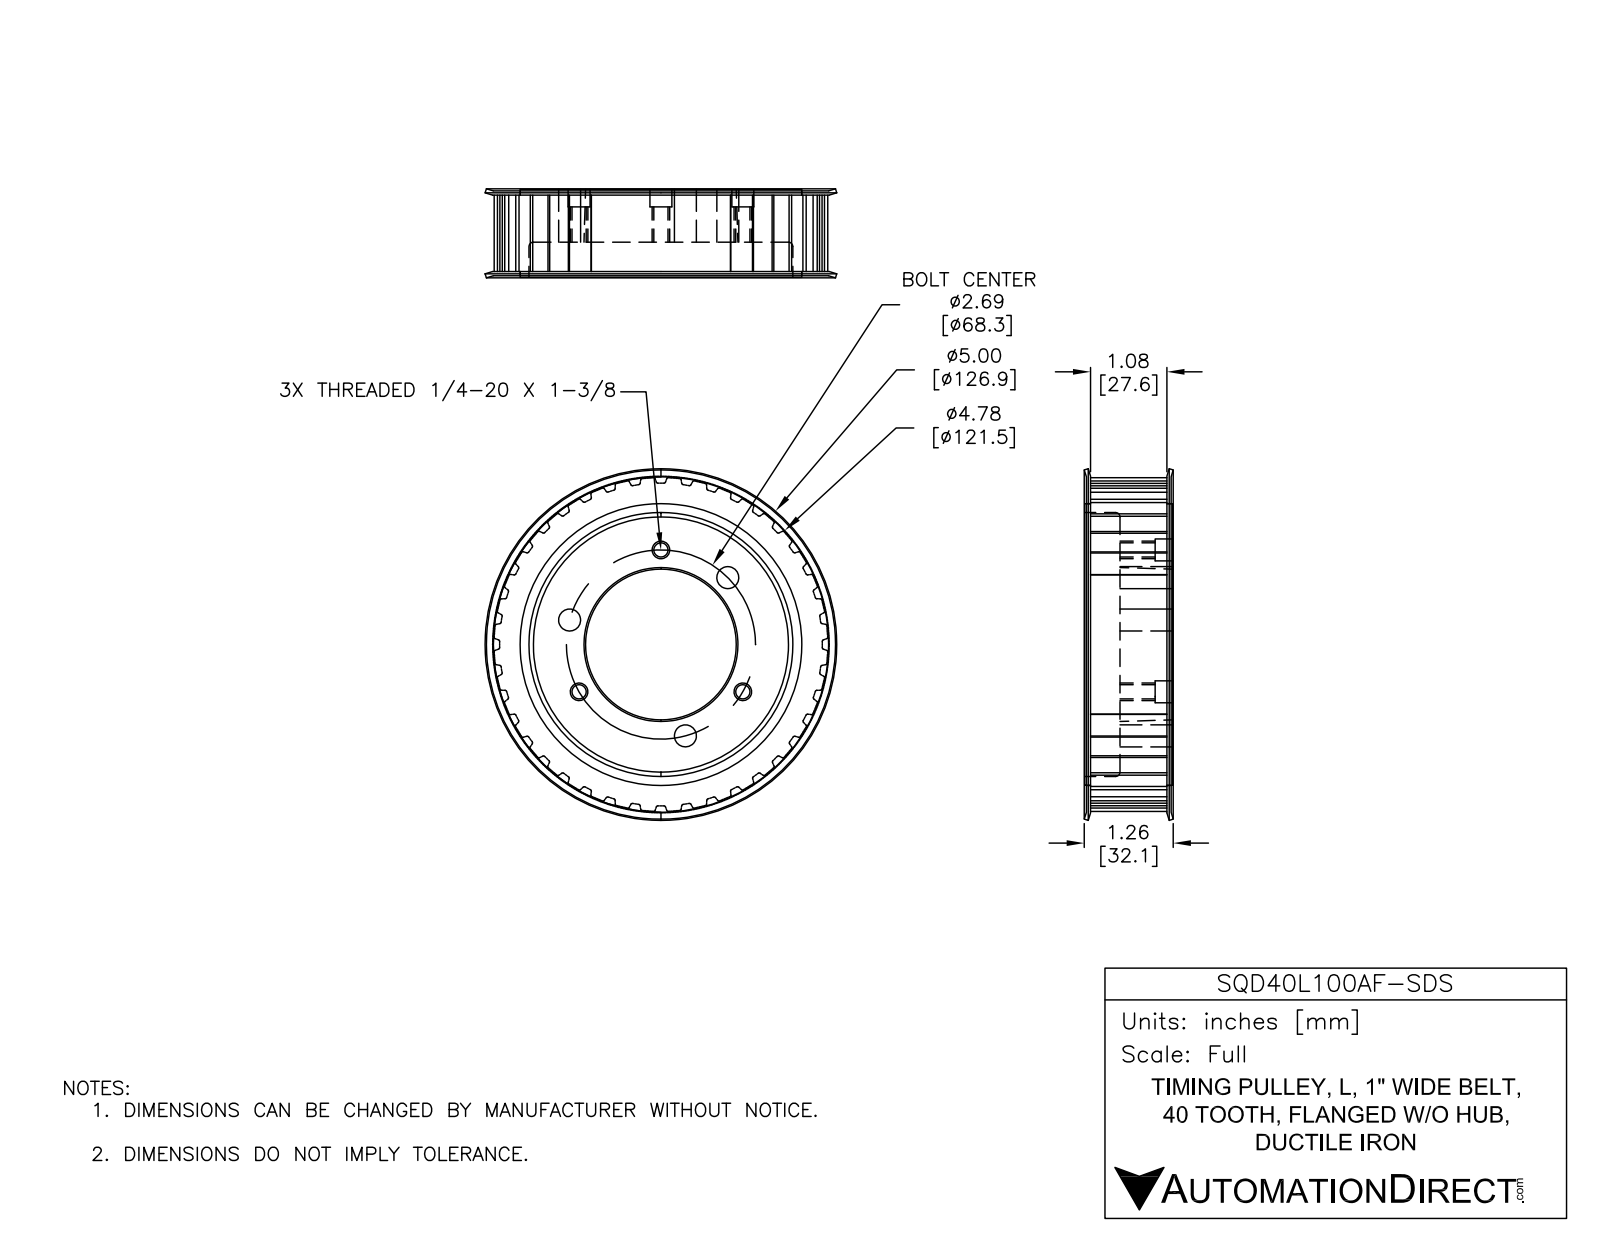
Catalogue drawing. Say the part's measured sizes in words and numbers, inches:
The part is named "SQD40L100AF-SDS". Its 3-D file was written by "SolidWorks 2018 (AUTOMOTIVE_DESIGN)". It is 4 solids with 406 faces: 132 planar, 258 cylindrical and 16 other. Overall it measures 4.997 by 4.997 by 1.265 inches. Its volume is 13.01 cubic inches and its surface area 121.6 square inches. Round holes: 6 of diameter 0.313, 3 of diameter 0.201, 1 of diameter 3.75, 1 of diameter 4, 1 of diameter 4.004. Partial cylindrical surfaces (rounded edges, fillets, slot ends): 80 of radius 0.021, 80 of radius 0.04, 1 of radius 2.374. The main face-to-face distances are 1.085, 0.083, 1.168, 0.022, 1.228, 0.75, 0.667, 0.418, 1.145, 0.478. The hole center spacings are 1.344, 2.328, 2.665, 1.028, 1.636, 1.029, 1.636, 2.327.
